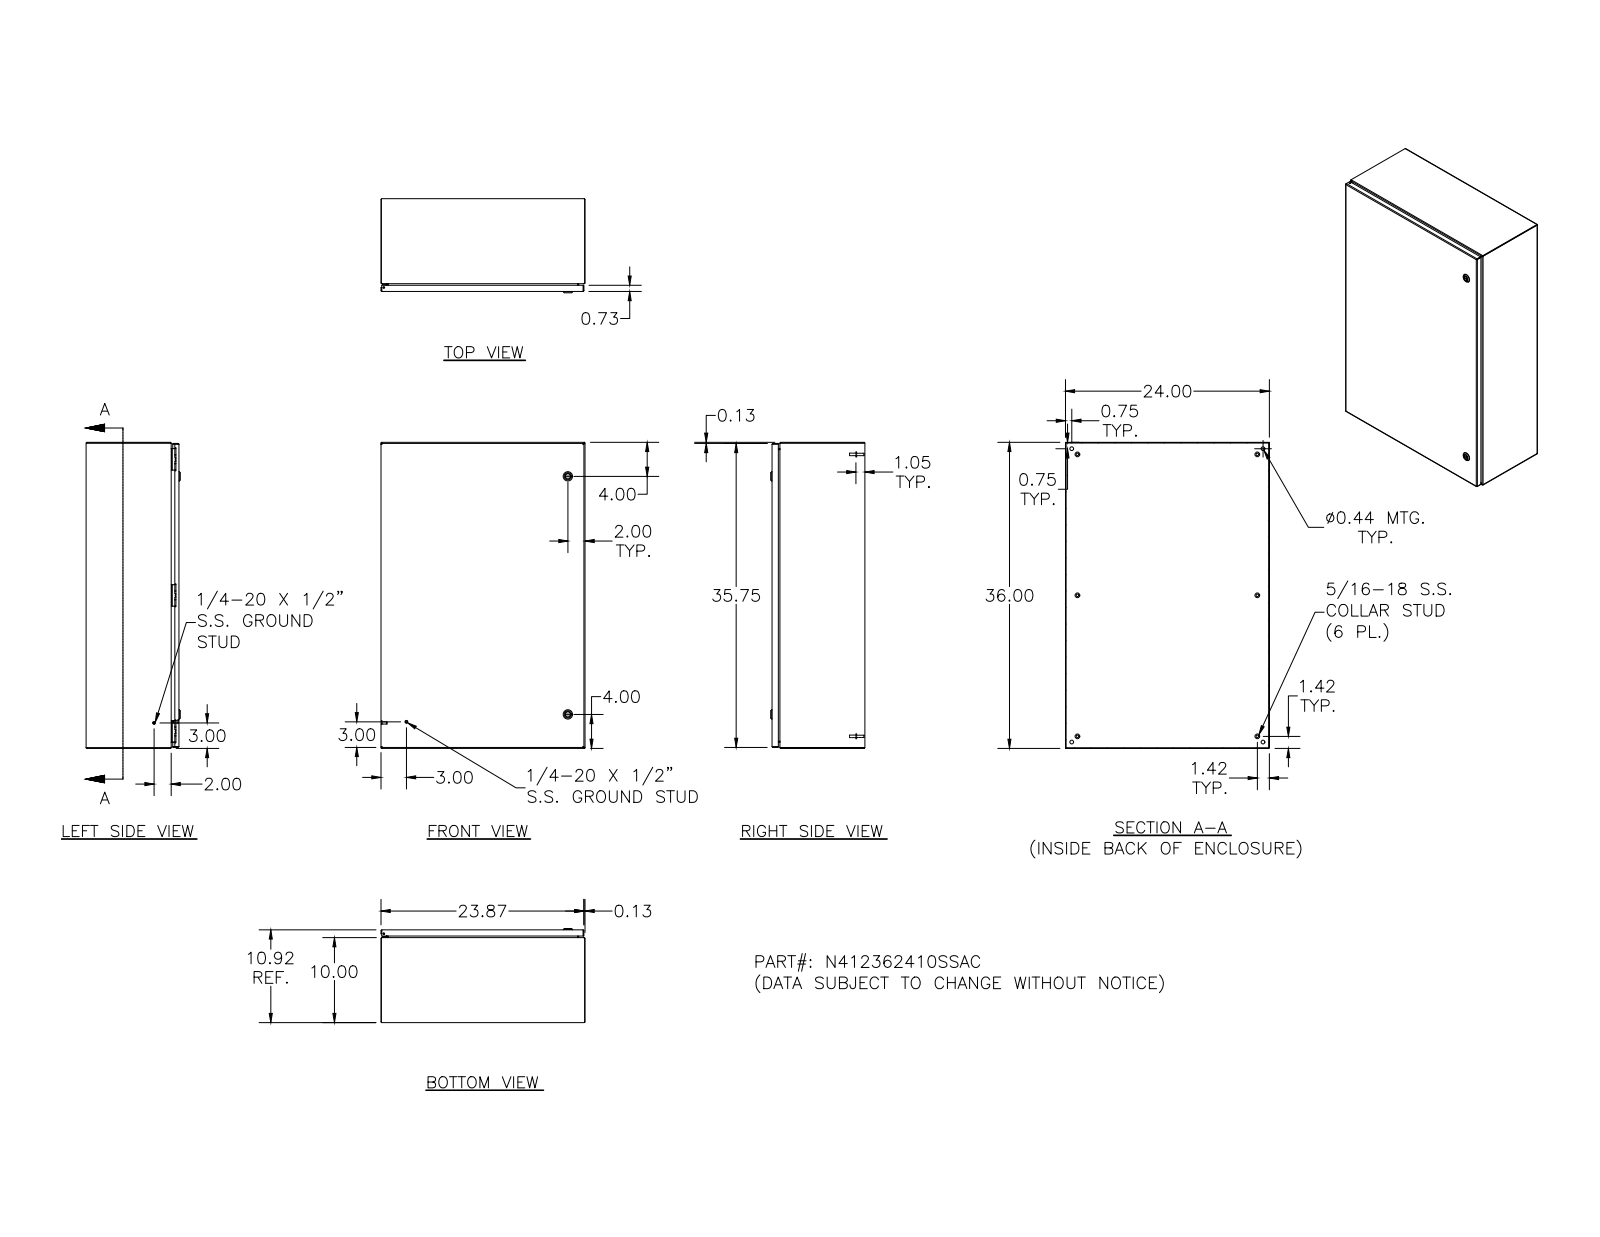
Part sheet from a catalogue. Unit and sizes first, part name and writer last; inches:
Units: inches
Overall size (bounding box): 36 × 24 × 11.075
Round holes (diameter × count): ⌀0.188 ×7, ⌀0.093 ×6, ⌀0.152 ×6, ⌀0.167 ×6, ⌀0.172 ×6, ⌀0.437 ×4, ⌀0.156 ×3, ⌀0.197 ×2, ⌀0.315 ×2, ⌀0.394 ×2, ⌀0.402 ×2, ⌀0.634 ×2
Round bosses / shafts (diameter × count): ⌀0.25 ×14, ⌀0.563 ×6, ⌀0.36 ×6, ⌀0.32 ×6, ⌀0.3 ×6, ⌀0.275 ×6, ⌀0.256 ×6, ⌀0.164 ×6
Partial cylindrical surfaces — rounded edges, fillets, slot ends (radius × count): R0.05 ×38, R0.016 ×26, R0.125 ×21, R0.031 ×18, R0.016 ×16, R0.09 ×16, R0.02 ×15, R0.032 ×12
Main face-to-face distances: 0.074, 10.843, 10.769, 10.917, 23.926, 35.926, 23.852, 24, 36, 35.852
Hole centre spacings: 16.004, 32, 15.996, 0.017, 0.66, 15.992, 16, 16.008
Volume: 235.6 in³ · Surface area: 6 392 in²
Bodies: 53 solids, 2098 faces (823 planar, 766 cylindrical, 509 other)
Part name (STEP PRODUCT): N412362410SSAC; N412362410SSACBKP; 388151; N4123624SSACLID (+8 more)
STEP written by: Autodesk Inventor 2011 (AUTOMOTIVE_DESIGN)
